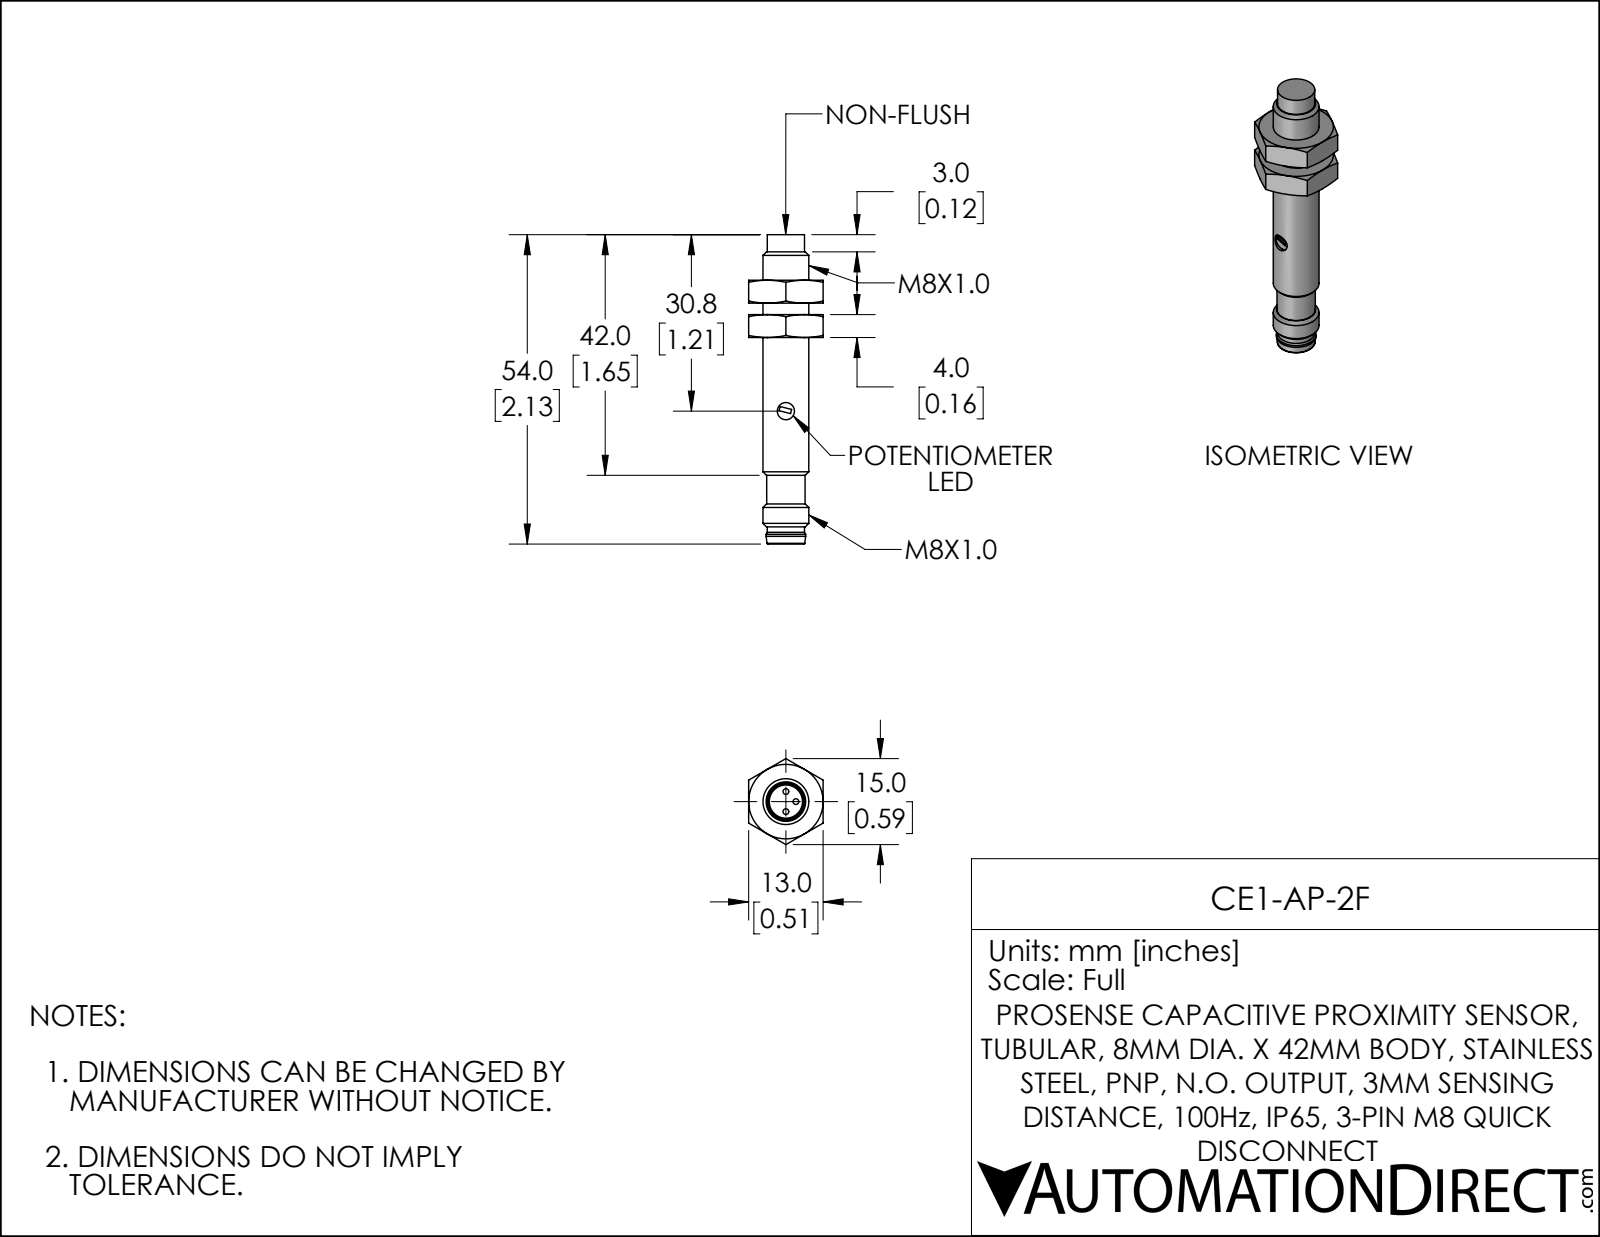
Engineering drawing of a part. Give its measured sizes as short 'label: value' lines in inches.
name: CE1-AP-2F
written by: SolidWorks 2019 (CONFIG_CONTROL_DESIGN)
unit: in
bodies: 3 solids, 80 faces (31 planar, 13 cylindrical, 36 other)
size: 2.126 × 0.591 × 0.512
volume: 0.198 in³; area: 3.819 in²
holes: 1× ⌀0.118, 1× ⌀0.228, 1× ⌀0.272
bosses: 3× ⌀0.039, 1× ⌀0.315, 1× ⌀0.272, 1× ⌀0.264, 1× ⌀0.256
face distances: 0.512, 0.157, 0.236, 0.079, 0.394, 0.313, 0.47, 0.549, 0.707, 1.459
